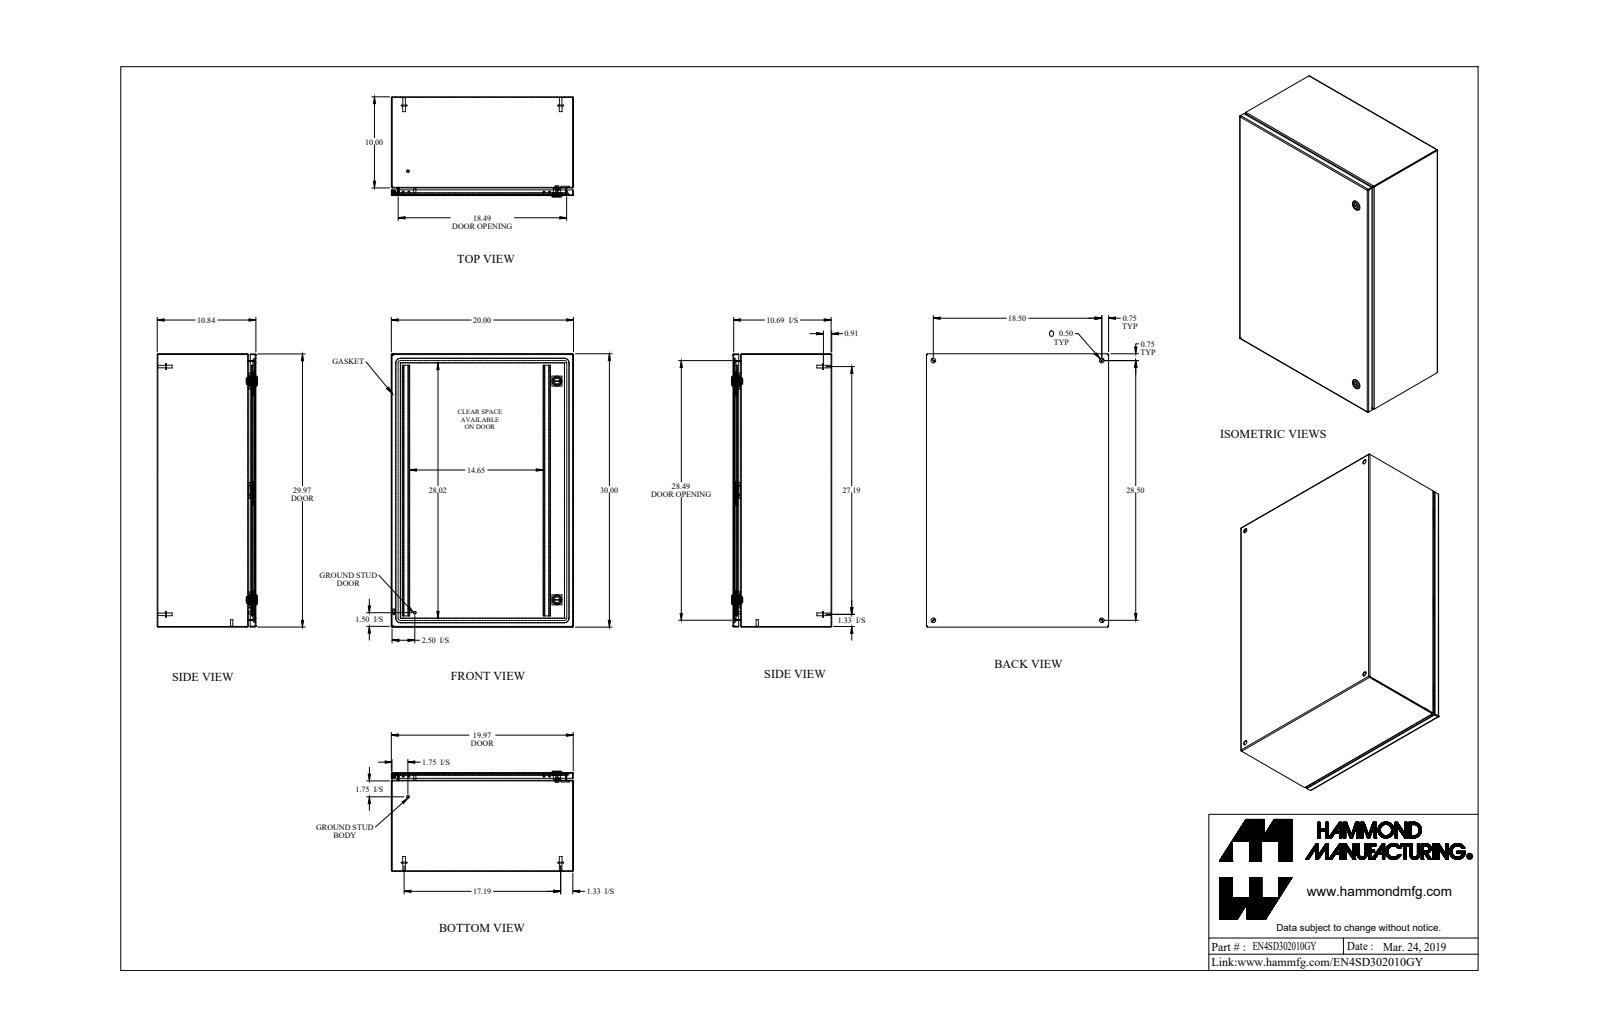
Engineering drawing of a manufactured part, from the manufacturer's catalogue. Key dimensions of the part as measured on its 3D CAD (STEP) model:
Part name (STEP PRODUCT): EN4SD302010GY
STEP written by: SolidWorks 2019 (AUTOMOTIVE_DESIGN)
Units: inches
Bodies: 31 solids, 854 faces (395 planar, 295 cylindrical, 164 other)
Overall size (bounding box): 30 × 20 × 10.997
Volume: 186.1 in³ · Surface area: 5 229 in²
Round holes (diameter × count): ⌀0.5 ×4, ⌀0.232 ×2, ⌀0.625 ×2, ⌀0.785 ×2, ⌀0.172 ×1, ⌀0.24 ×1, ⌀0.242 ×1
Round bosses / shafts (diameter × count): ⌀0.625 ×4, ⌀0.313 ×4, ⌀0.27 ×4, ⌀1.1 ×2, ⌀0.525 ×2, ⌀0.281 ×2, ⌀0.25 ×2, ⌀0.455 ×1
Partial cylindrical surfaces — rounded edges, fillets, slot ends (radius × count): R0.036 ×16, R0.108 ×16, R0.043 ×12, R0.081 ×12, R0.382 ×12, R0.1 ×8, R19.003 ×8, R0.006 ×6
Main face-to-face distances: 0.072, 10.765, 10.693, 10.837, 19.928, 29.928, 19.856, 20, 29.856, 30
Hole centre spacings: 18.5, 28.5, 33.978, 2.493, 2.494, 17.572, 17.572, 23.999
